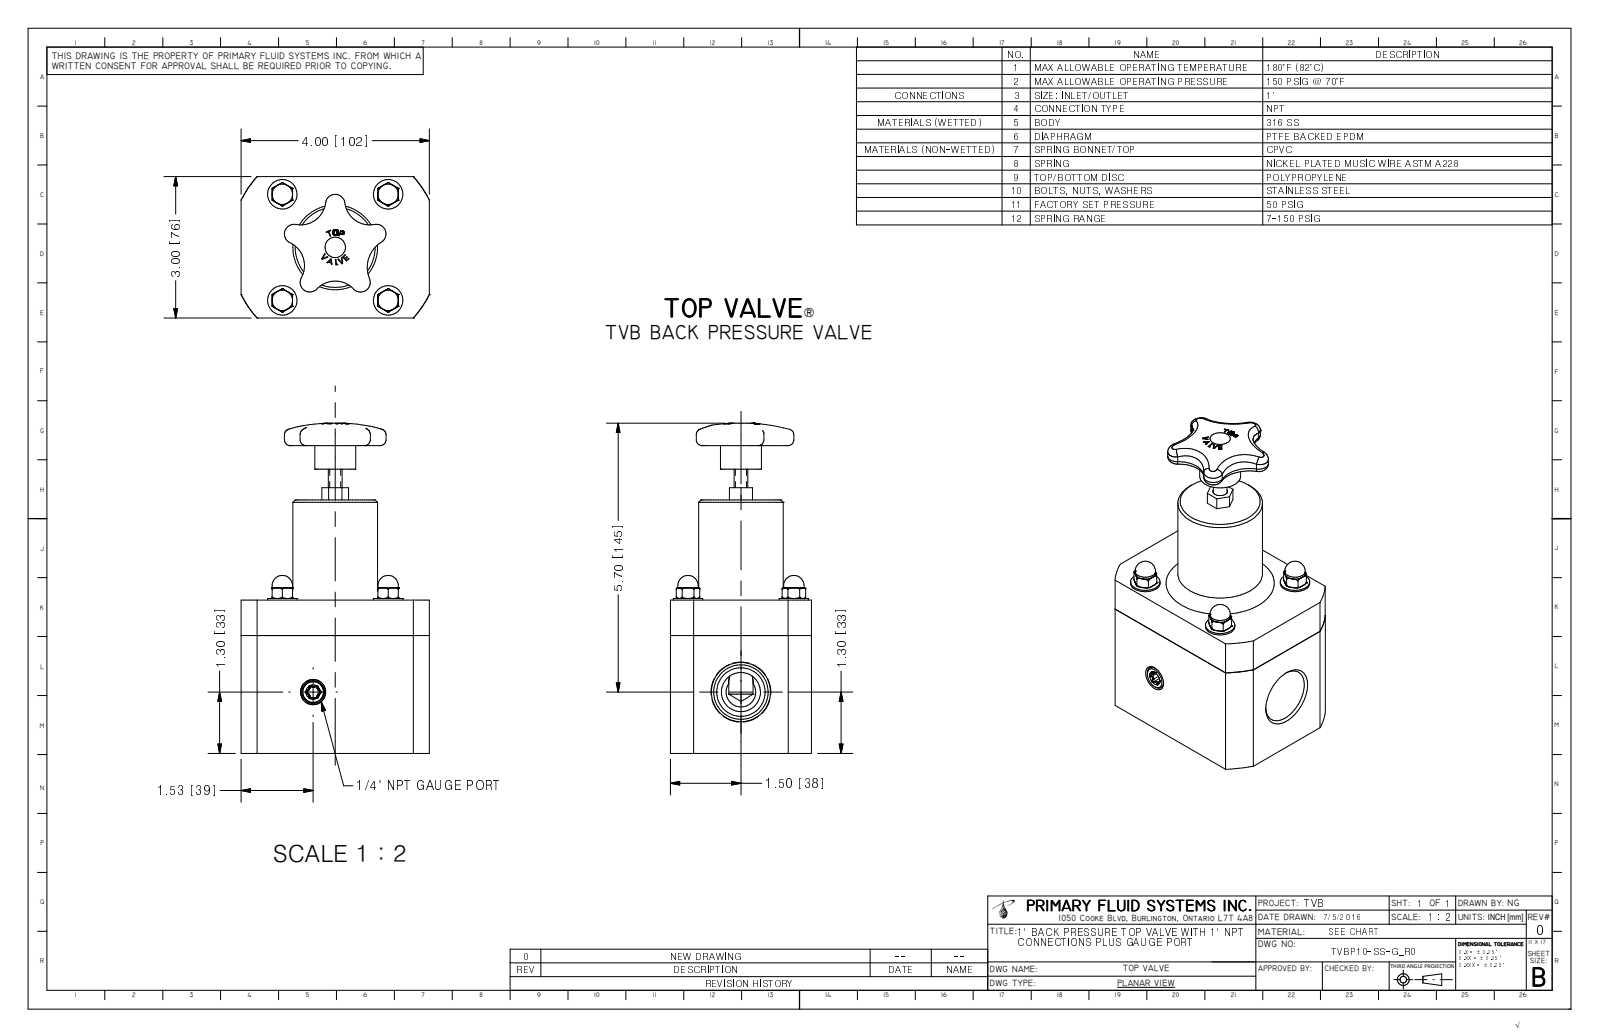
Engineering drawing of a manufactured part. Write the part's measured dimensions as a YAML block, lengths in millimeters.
part_name: "TVBP10-SS-G-R0"
step_written_by: "Autodesk Inventor 2009 (AUTOMOTIVE_DESIGN)"
units: millimeters
bodies: {solids: 1, faces: 367, planar: 156, cylindrical: 55, other: 156}
overall_size: [177.9, 101.6, 76.2]
volume: 701900
surface_area: 64970
round_holes:
  - {diameter: 4.4, count: 4}
  - {diameter: 29.4, count: 1}
round_bosses_or_shafts:
  - {diameter: 15.9, count: 4}
  - {diameter: 11, count: 4}
  - {diameter: 9.5, count: 4}
  - {diameter: 45.7, count: 1}
  - {diameter: 22.1, count: 1}
  - {diameter: 7.4, count: 1}
partial_cylinders:
  - {radius: 0.7, count: 6}
  - {radius: 2.2, count: 5}
  - {radius: 5.2, count: 5}
  - {radius: 13.6, count: 4}
  - {radius: 16.7, count: 4}
  - {radius: 15.9, count: 1}
  - {radius: 18.9, count: 1}
  - {radius: 56.8, count: 1}
face_to_face_distances: [76.2, 82.6, 101.6, 25.4, 136.5, 54, 50.8, 83.5, 0.9, 53.1]
hole_center_spacings: [57.2, 80.8]
